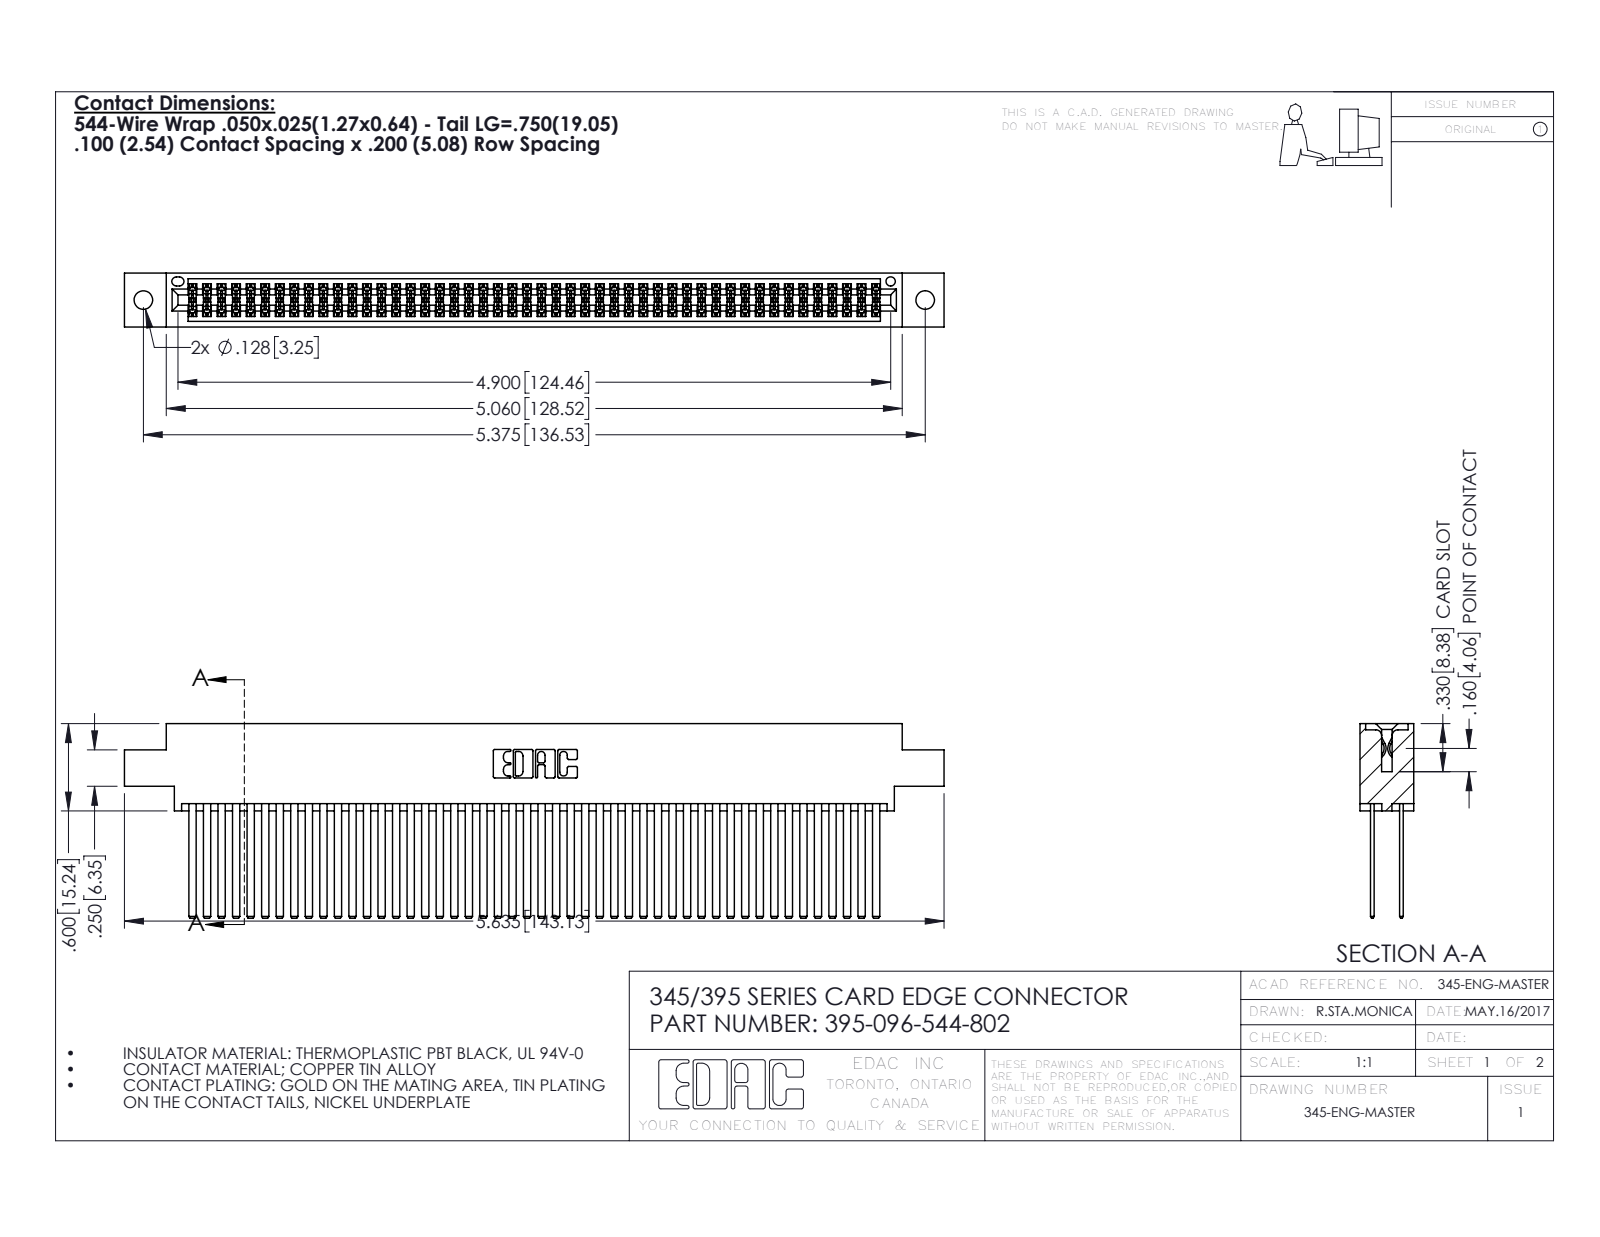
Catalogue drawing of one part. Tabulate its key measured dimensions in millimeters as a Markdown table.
| quantity | value |
| --- | --- |
| part name | 345 Part_0.170 Offset - 0.128 Dia; 345-292-001_345-293-144; 395-096-544-802 |
| STEP written by | SolidWorks 2016 (CONFIG_CONTROL_DESIGN) |
| units | millimeters |
| bodies | 97 solids, 4354 faces (2868 planar, 1486 cylindrical, 0 other) |
| overall size | 143.1 × 34 × 9.4 |
| volume | 15 200 mm³ |
| surface area | 26 340 mm² |
| round holes (diameter × count) | 3.3 × 2, 1.6 × 1 |
| partial cylindrical surfaces (radius × count) | 0.2 × 144, 0.3 × 22, 0.2 × 6, 0.8 × 6, 0.7 × 3, 0.4 × 2, 0.5 × 2, 0.6 × 2 |
| main face-to-face distances | 5.1, 0.6, 7.6, 1.8, 2.5, 6.9, 5.7, 4.4, 9.4, 3.8 |
| hole center spacings | 6.9, 130.5, 136.5 |
